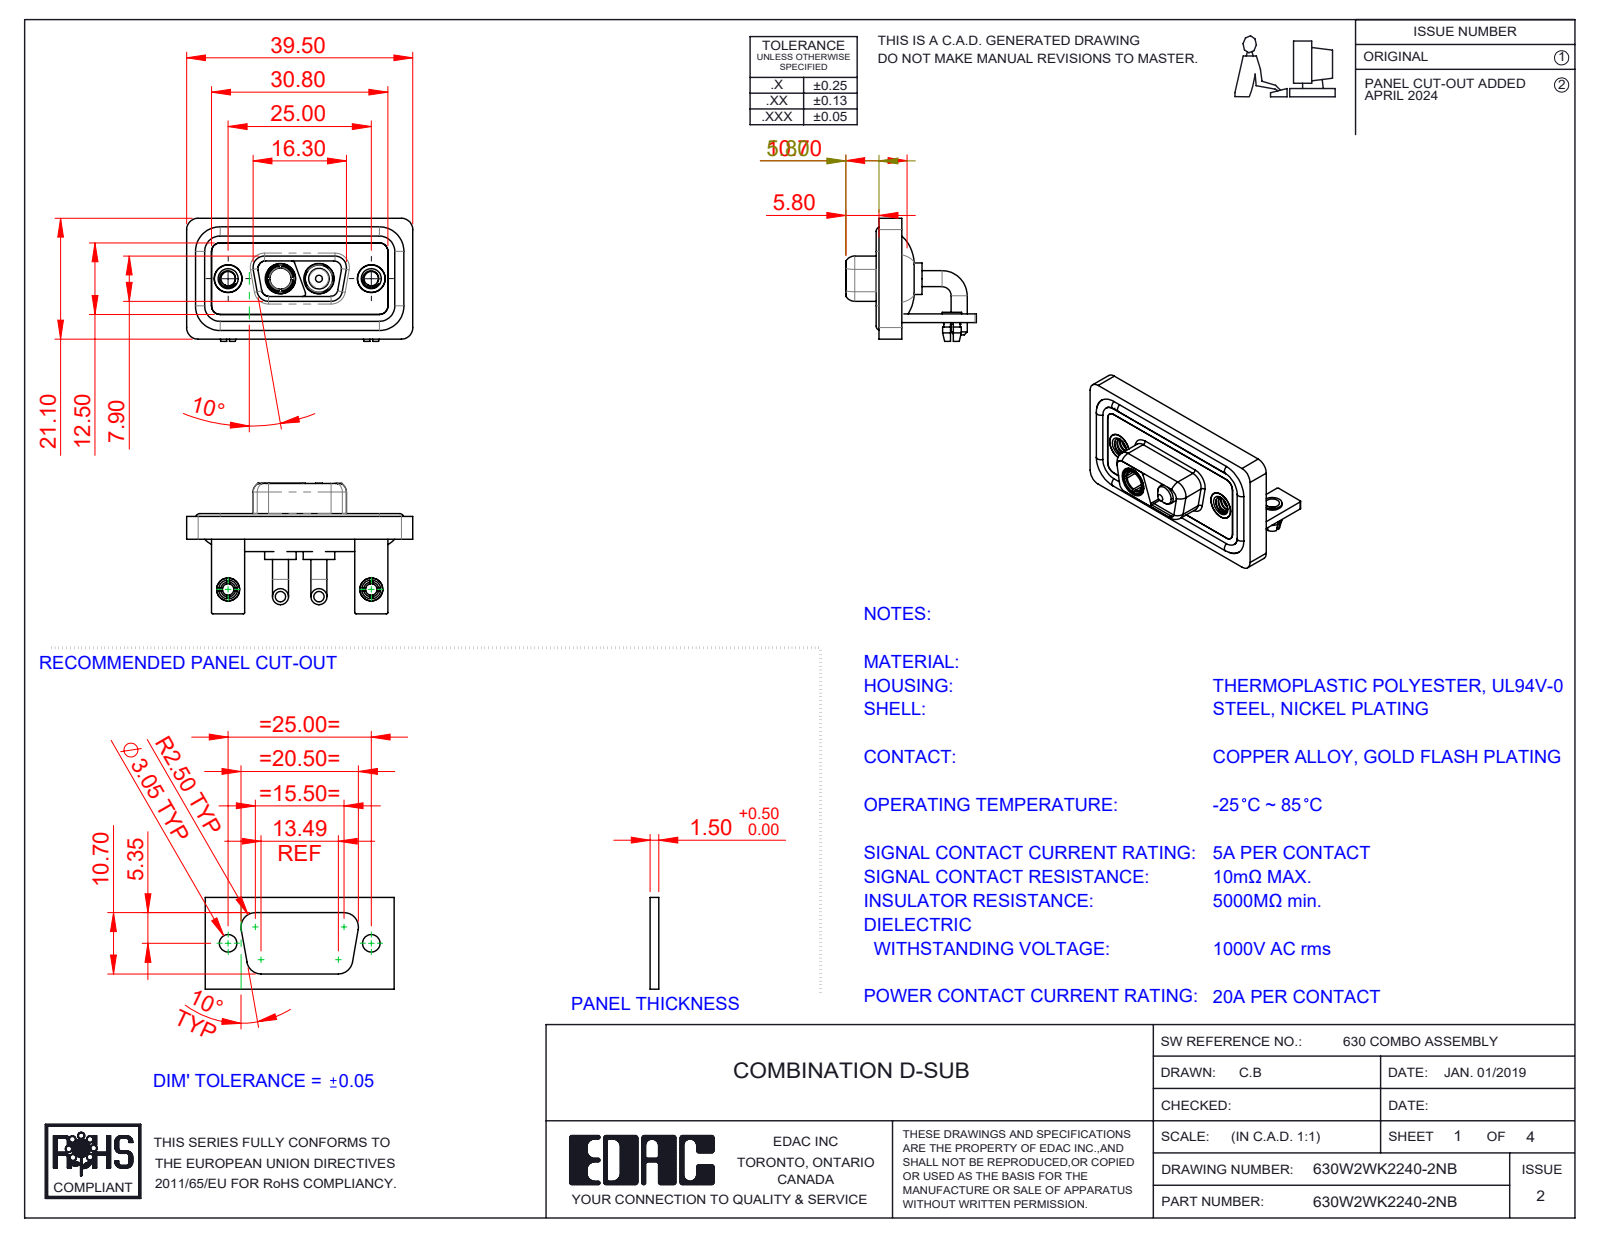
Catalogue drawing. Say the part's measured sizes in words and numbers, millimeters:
The part is named "630Combo Shell Rear_09 Contacts; 630W2WK2240-2NB; Power Socket_20A RA; 630Combo Board Lock_50 Contacts (+6 more)". Its 3-D file was written by "SolidWorks 2023 (CONFIG_CONTROL_DESIGN)". It is 15 solids with 642 faces: 212 planar, 289 cylindrical and 141 other. Overall it measures 39.5 by 22.8 by 21.5 millimeters. Its volume is 5 102 cubic millimeters and its surface area 8 443 square millimeters. Round holes: 4 of diameter 2.5, 4 of diameter 4.85, 2 of diameter 2, 2 of diameter 3.2, 2 of diameter 4, 2 of diameter 4.05, 2 of diameter 5, 2 of diameter 5.3, 1 of diameter 3.7. Round bosses or shafts: 4 of diameter 2.8, 4 of diameter 1.6, 2 of diameter 5.5, 2 of diameter 5.2, 2 of diameter 4.95, 2 of diameter 4.8, 2 of diameter 4.75, 2 of diameter 4. Partial cylindrical surfaces (rounded edges, fillets, slot ends): 19 of radius 2, 18 of radius 1.5, 16 of radius 0.25, 8 of radius 1.35, 8 of radius 1.6, 7 of radius 0.5, 4 of radius 0.6, 4 of radius 0.65. The main face-to-face distances are 0.4, 2.9, 1.5, 1.1, 3.7, 1.8, 0.8, 2.5, 1.6, 3.1. The hole center spacings are 9.14, 15.86, 25, 6.72.
